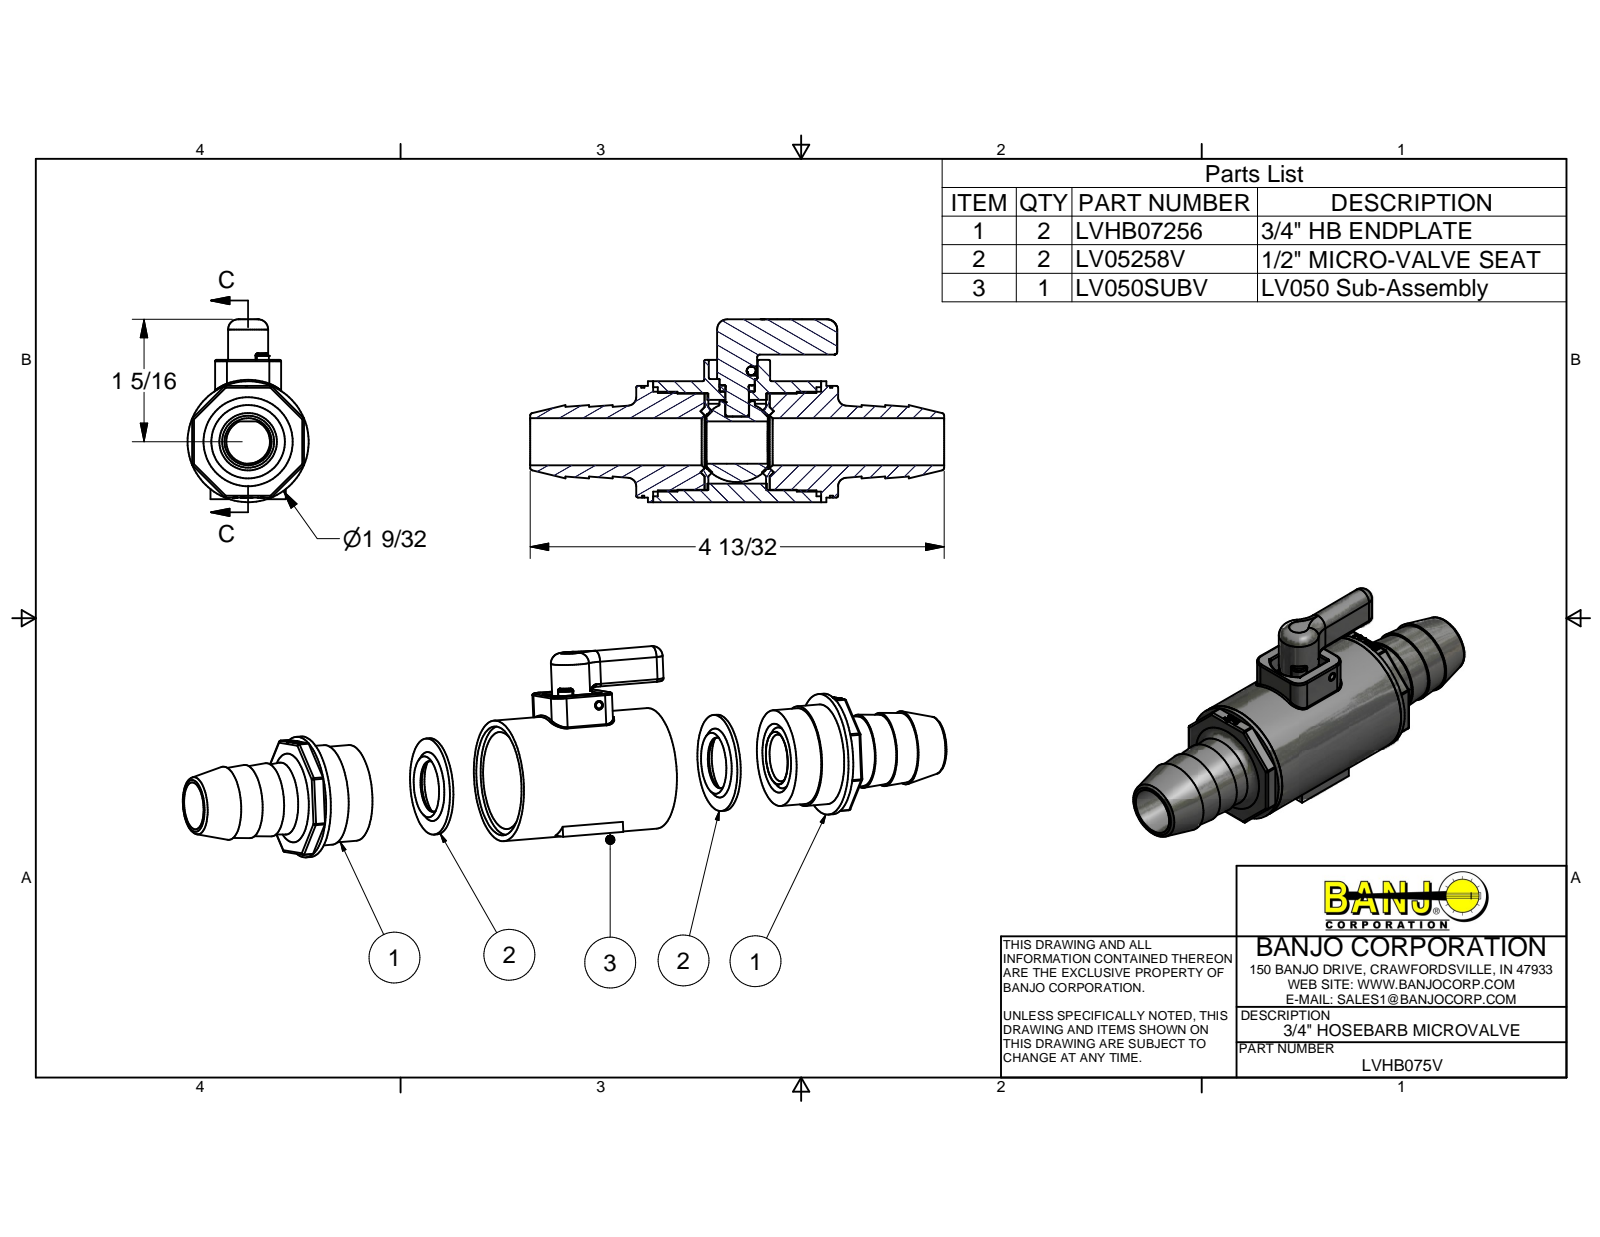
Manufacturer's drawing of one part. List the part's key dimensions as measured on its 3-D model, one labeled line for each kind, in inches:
Part name (STEP PRODUCT): LVHB075V; LV050SUBV; LV05254A; LV02153B (+5 more)
STEP written by: Autodesk Inventor 2012 (AUTOMOTIVE_DESIGN)
Units: inches
Bodies: 9 solids, 682 faces (288 planar, 131 cylindrical, 263 other)
Overall size (bounding box): 4.392 × 1.944 × 1.285
Volume: 3.024 in³ · Surface area: 44.71 in²
Round holes (diameter × count): ⌀0.093 ×1, ⌀0.251 ×1, ⌀0.368 ×1, ⌀0.376 ×1, ⌀0.47 ×1, ⌀0.5 ×1, ⌀0.541 ×1, ⌀0.89 ×1, ⌀1.034 ×1, ⌀1.16 ×1
Round bosses / shafts (diameter × count): ⌀1.285 ×1, ⌀1.062 ×1, ⌀1.024 ×1, ⌀1.02 ×1, ⌀0.425 ×1, ⌀0.375 ×1, ⌀0.372 ×1, ⌀0.25 ×1
Partial cylindrical surfaces — rounded edges, fillets, slot ends (radius × count): R0.02 ×24, R0.01 ×16, R0.015 ×14, R0.125 ×4, R0.03 ×2, R0.05 ×2, R0.109 ×2, R0.25 ×2
Main face-to-face distances: 0.545, 1.237, 0.04, 0.692, 0.585, 1.197, 0.652, 0.18, 0.725, 0.765
